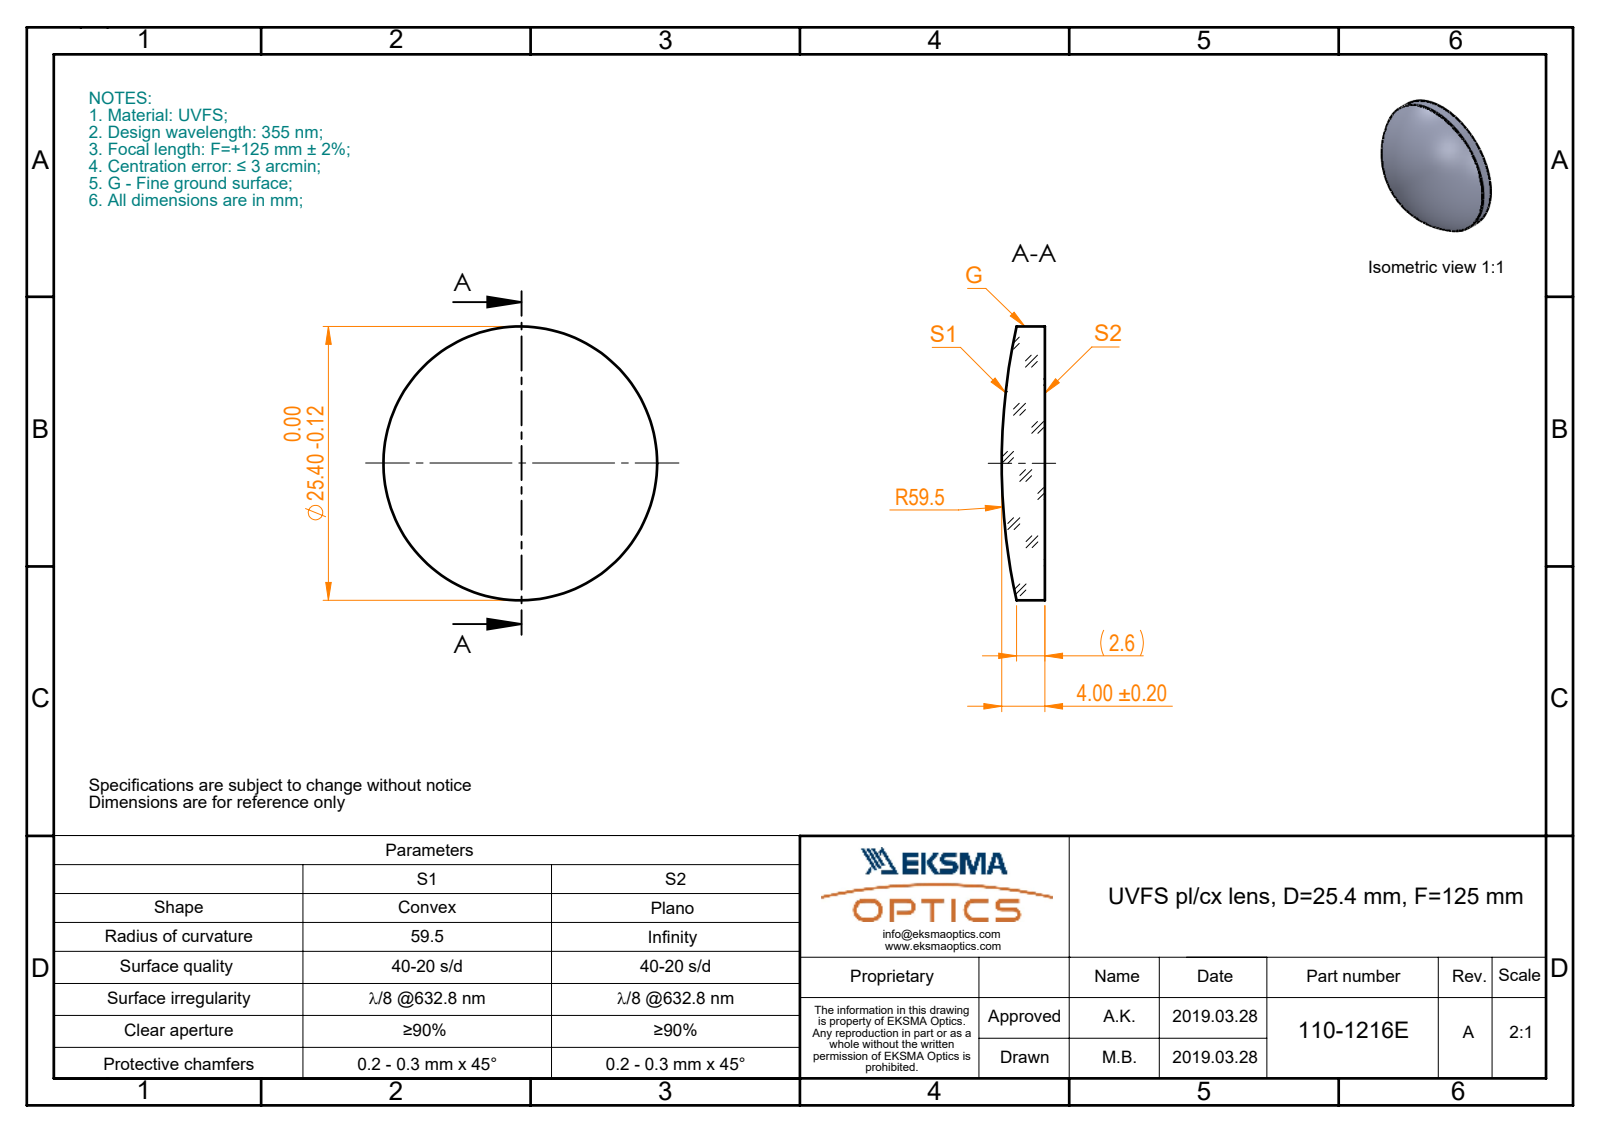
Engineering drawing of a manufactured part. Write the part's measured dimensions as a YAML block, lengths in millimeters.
part_name: "110-1216E UVFS pl-cx 25.4 F125"
step_written_by: "SolidWorks 2017 (CONFIG_CONTROL_DESIGN)"
units: millimeters
bodies: {solids: 1, faces: 5, planar: 1, cylindrical: 2, other: 2}
overall_size: [25.4, 25.4, 4]
volume: 1681
surface_area: 1229
round_bosses_or_shafts:
  - {diameter: 25.4, count: 1}
